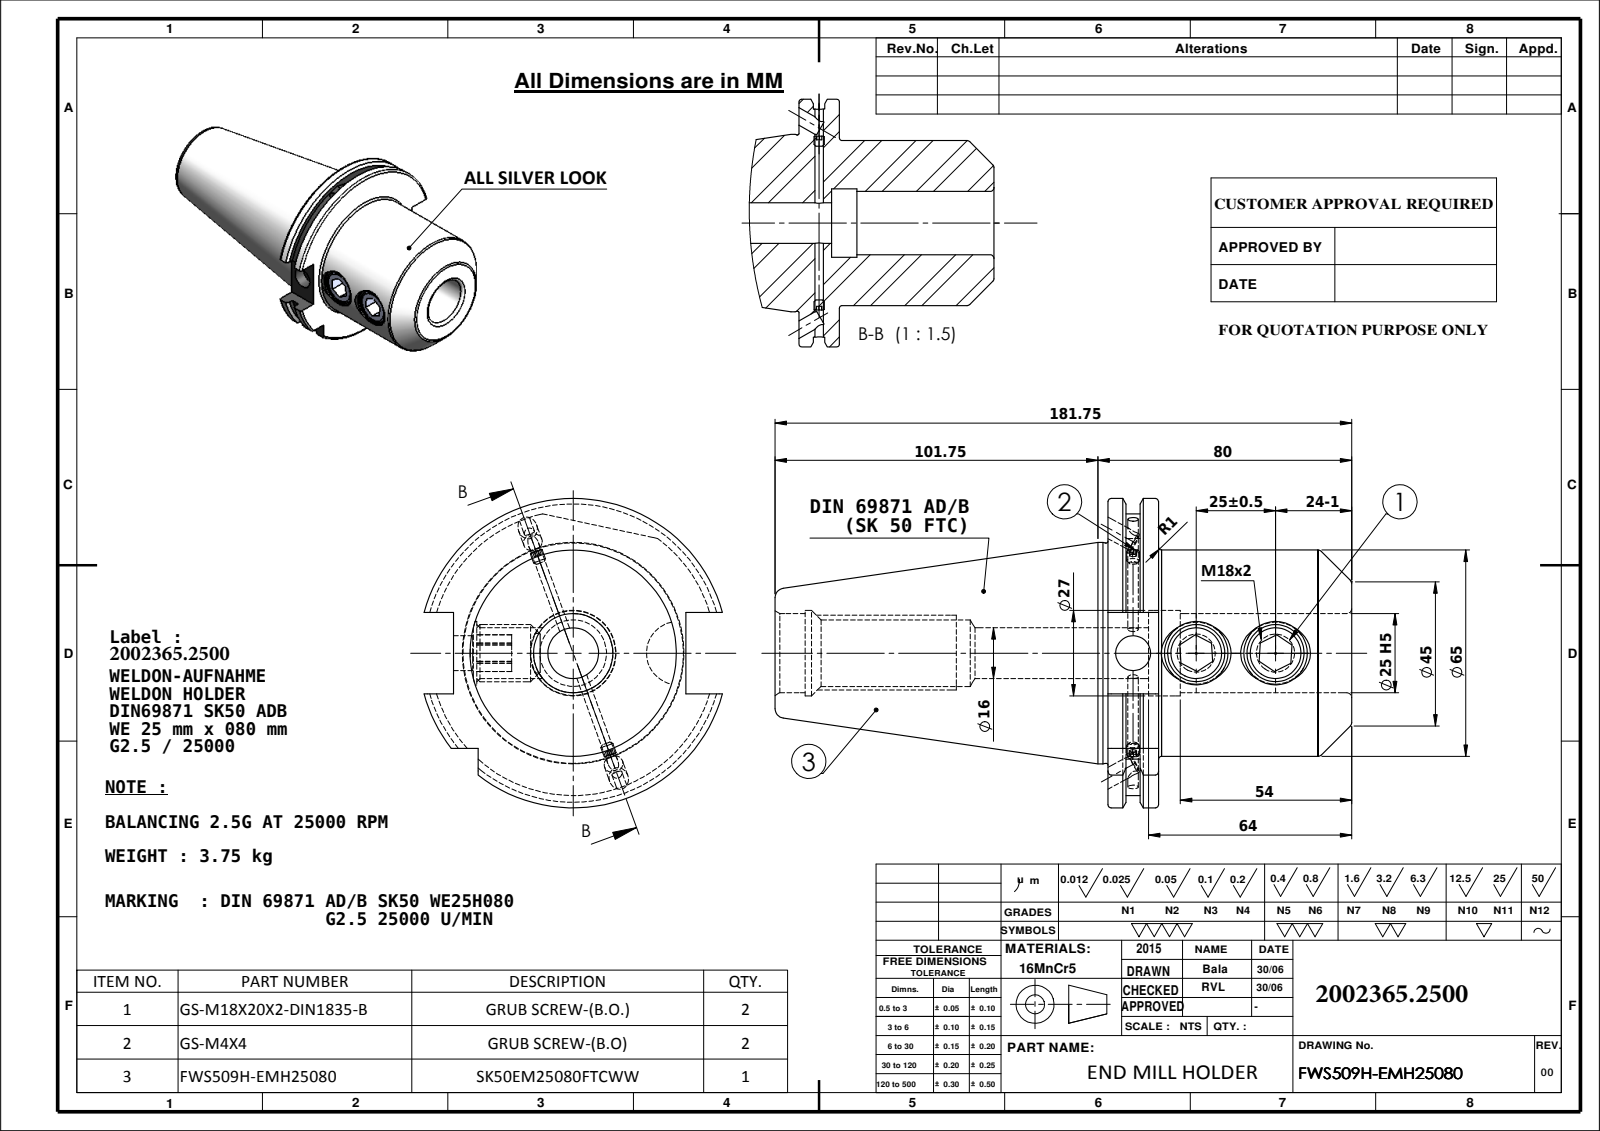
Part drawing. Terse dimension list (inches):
name: 91506-WE725080; SK50EM25080FTCWW; Copy of M4X4_DIN 913 - M4 x 4-N; GS-M18X2X20
written by: SolidWorks 2009 (CONFIG_CONTROL_DESIGN)
unit: in
bodies: 5 solids, 195 faces (64 planar, 61 cylindrical, 70 other)
size: 7.156 × 3.839 × 3.703
volume: 29.48 in³; area: 101.9 in²
holes: 3× ⌀0.63, 2× ⌀0.236, 2× ⌀0.787, 1× ⌀0.13, 1× ⌀0.433, 1× ⌀0.827, 1× ⌀0.984, 1× ⌀1.063
bosses: 2× ⌀0.709, 2× ⌀0.157, 1× ⌀2.75, 1× ⌀2.734, 1× ⌀2.559
rounds: 1× R1.768, 1× R1.919
face distances: 0.626, 3.024, 2.398, 0.223, 0.403, 2.801, 0.4, 0.177, 0.226, 2.624
hole spacings: 0.783, 0.984, 1.768
